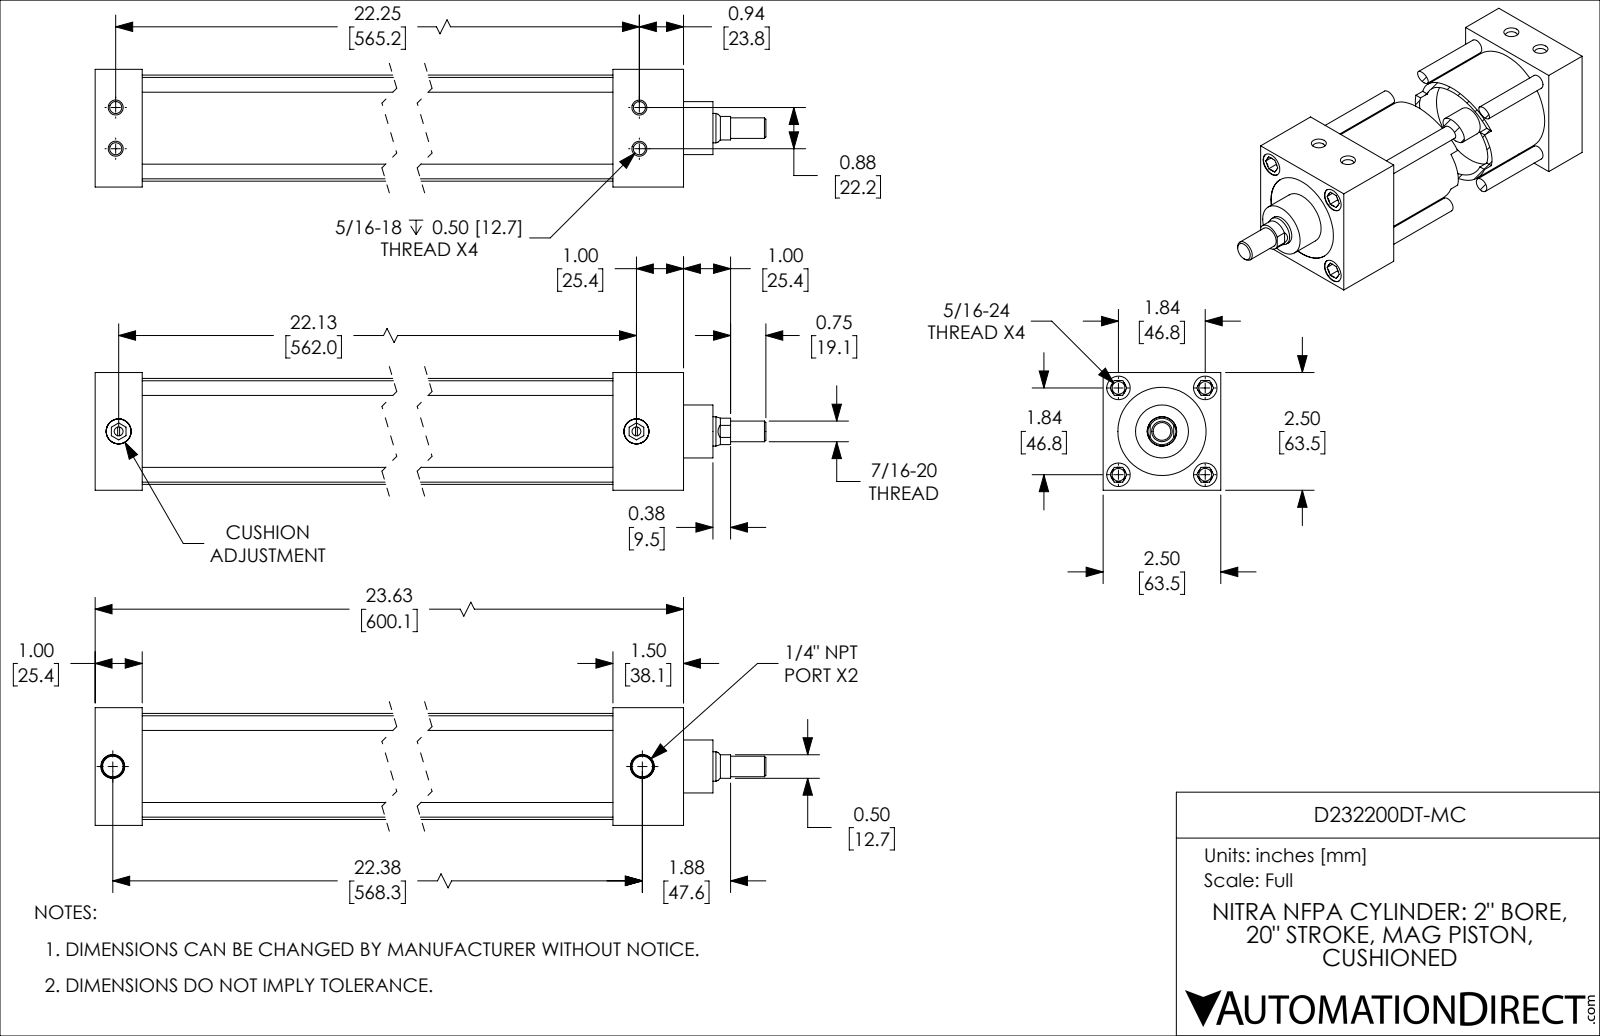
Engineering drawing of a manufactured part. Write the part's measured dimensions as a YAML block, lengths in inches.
part_name: "D232200DT-MC_PISTON_KK1; D232200DT-MC_CUSHION; D232200DT-MC_BODY; D232200DT-MC"
step_written_by: "SolidWorks 2019 (CONFIG_CONTROL_DESIGN)"
units: inches
bodies: {solids: 4, faces: 248, planar: 90, cylindrical: 78, other: 80}
overall_size: [25.375, 2.5, 2.5]
volume: 49.36
surface_area: 488.7
round_holes:
  - {diameter: 0.272, count: 7}
  - {diameter: 0.257, count: 4}
  - {diameter: 0.5, count: 4}
  - {diameter: 0.19, count: 2}
  - {diameter: 0.438, count: 2}
  - {diameter: 0.531, count: 2}
  - {diameter: 0.626, count: 1}
  - {diameter: 1.875, count: 1}
  - {diameter: 2.001, count: 1}
round_bosses_or_shafts:
  - {diameter: 0.312, count: 4}
  - {diameter: 0.532, count: 2}
  - {diameter: 2.251, count: 1}
  - {diameter: 1.999, count: 1}
  - {diameter: 1.125, count: 1}
  - {diameter: 0.624, count: 1}
  - {diameter: 0.437, count: 1}
partial_cylinders:
  - {radius: 0.281, count: 1}
face_to_face_distances: [2.5, 1, 22.125, 21.125, 2.125, 1.125, 20, 23.625, 22.625, 21.5]
hole_center_spacings: [1.84, 1.844, 1.301, 0.441, 0.443, 0.875, 1.304, 2.602]
